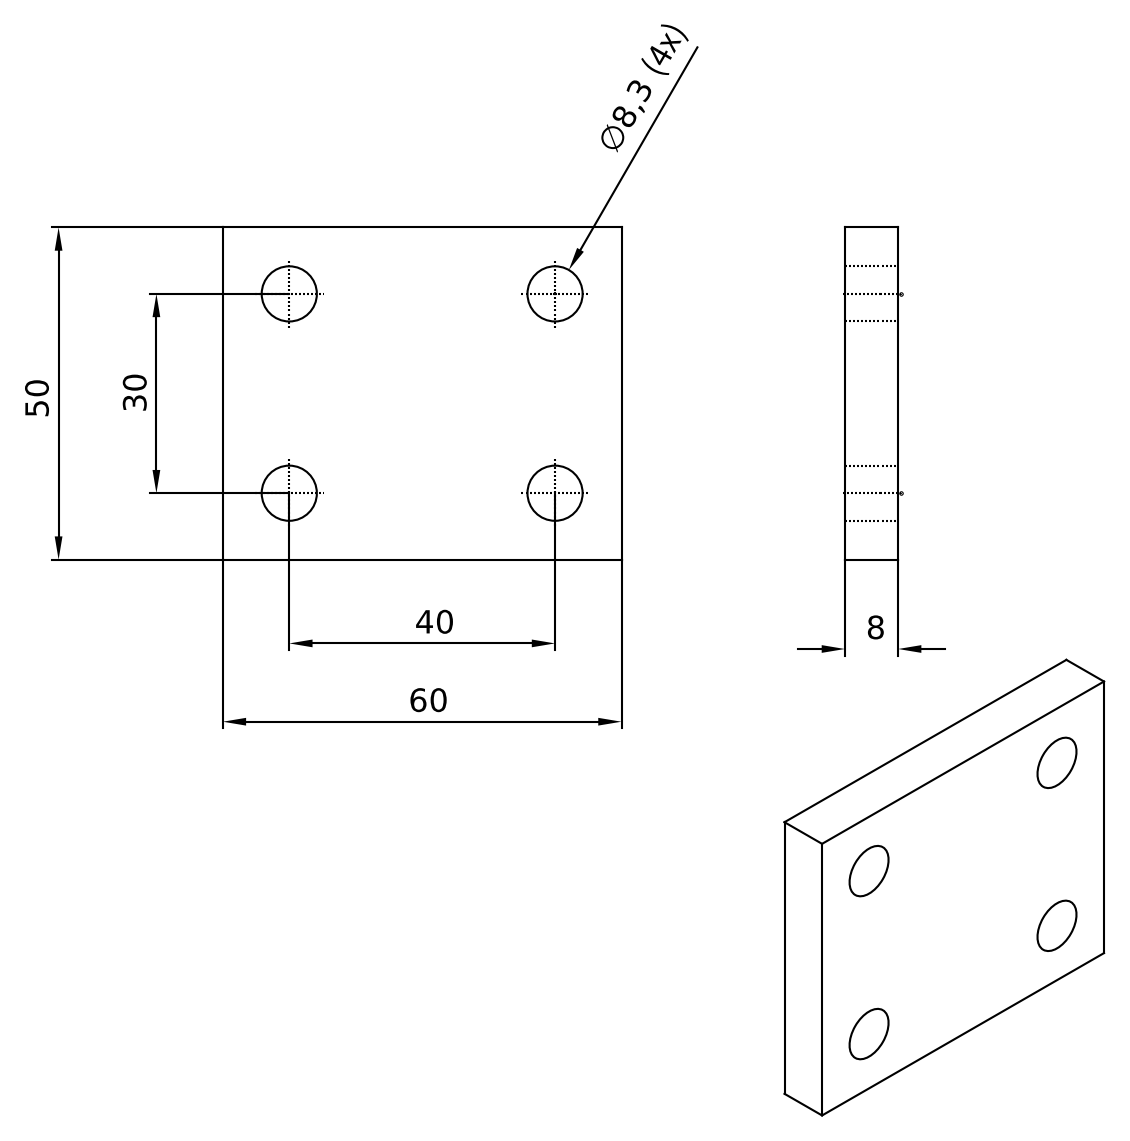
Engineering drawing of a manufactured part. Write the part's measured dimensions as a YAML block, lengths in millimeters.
part_name: "615-25E1"
step_written_by: "Autodesk Inventor 8 (AUTOMOTIVE_DESIGN)"
units: millimeters
bodies: {solids: 1, faces: 14, planar: 6, cylindrical: 0, other: 8}
overall_size: [60, 50, 8]
volume: 22269
surface_area: 8161
face_to_face_distances: [8, 50, 60]
